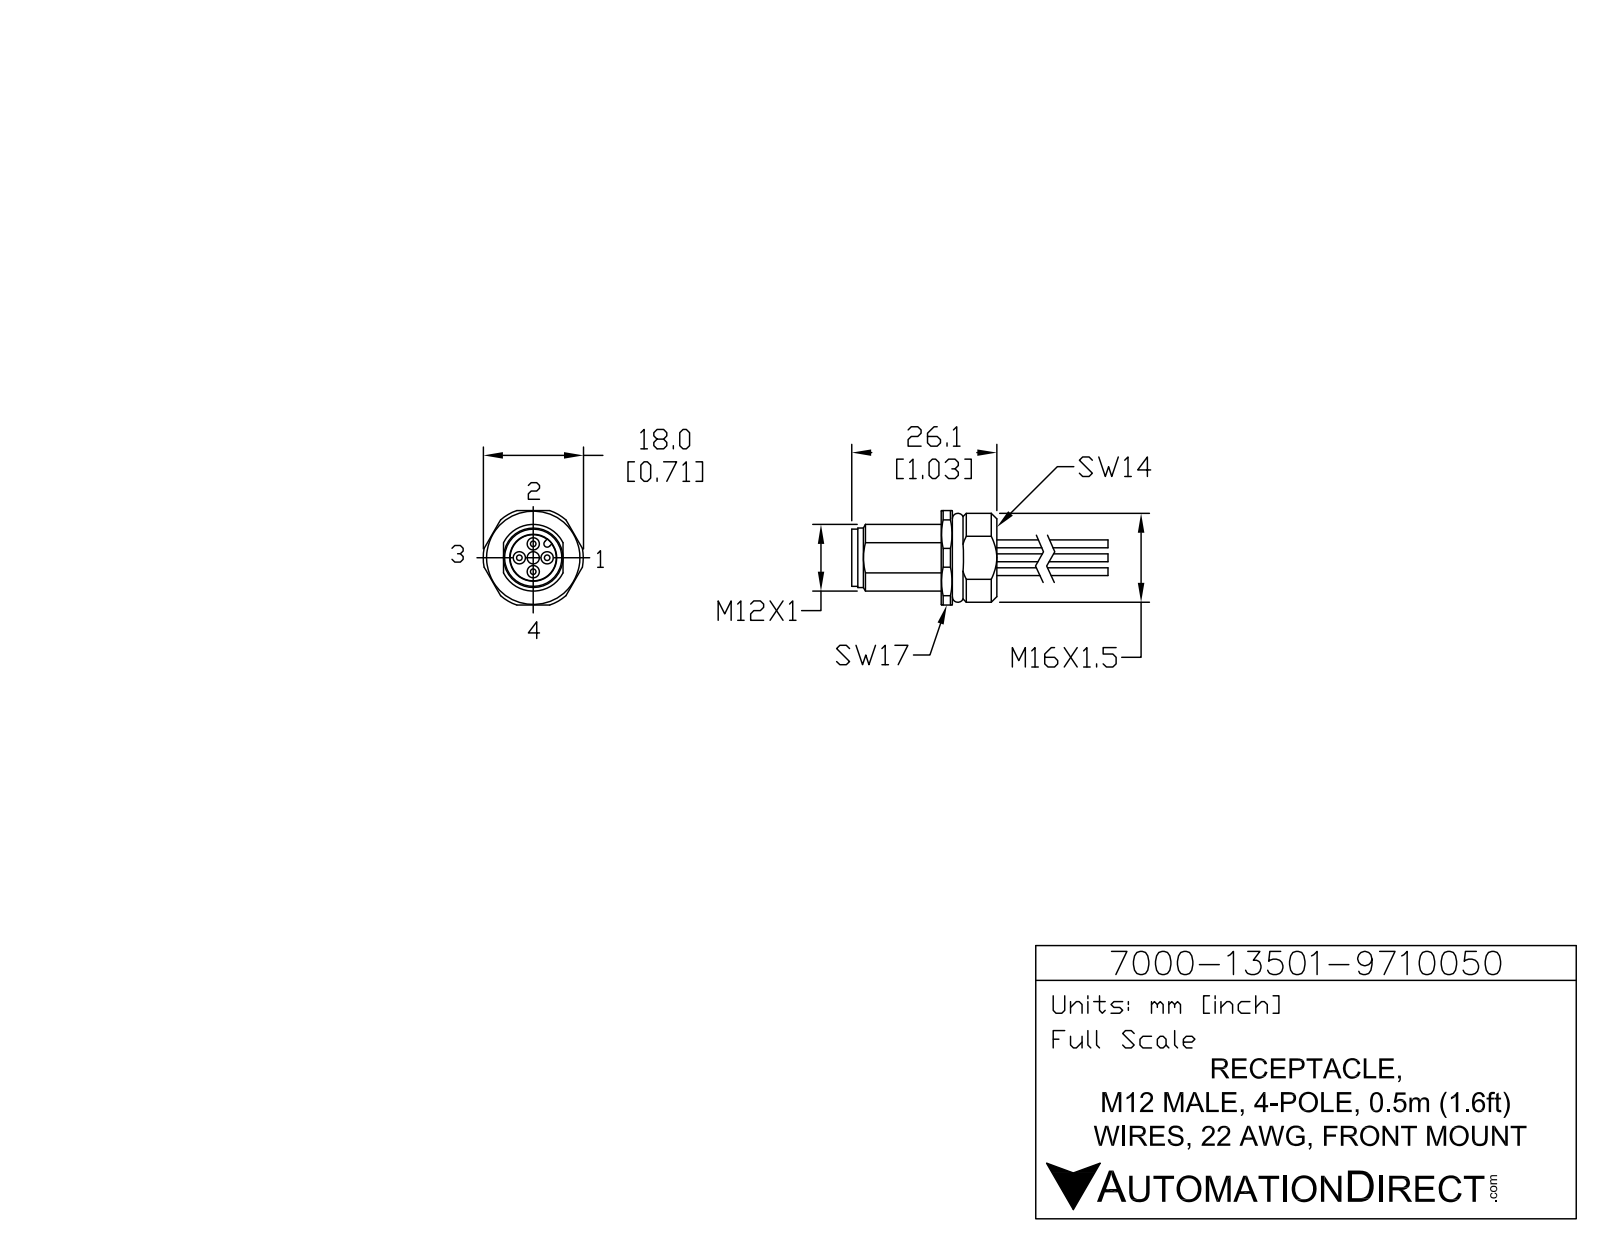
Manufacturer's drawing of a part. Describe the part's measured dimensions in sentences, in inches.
The part is named "7231-13501-9710050". Its 3-D file was written by "SolidWorks 2015 (AUTOMOTIVE_DESIGN)". It is 1 solid with 101 faces: 33 planar, 44 cylindrical and 24 other. Overall it measures 1.815 by 0.709 by 0.669 inches. Its volume is 0.196 cubic inches and its surface area 3.684 square inches. Round holes: 5 of diameter 0.087, 1 of diameter 0.512. Round bosses or shafts: 4 of diameter 0.055, 4 of diameter 0.039, 1 of diameter 0.421, 1 of diameter 0.406. Partial cylindrical surfaces (rounded edges, fillets, slot ends): 1 of radius 0.024, 1 of radius 0.236, 1 of radius 0.315, 1 of radius 0.354. The main face-to-face distances are 0.354, 0.065, 0.486, 0.421, 0.079, 0.276, 0.551, 0.669, 0.638, 0.362. The hole center spacings are 0.098, 0.139, 0.197.
